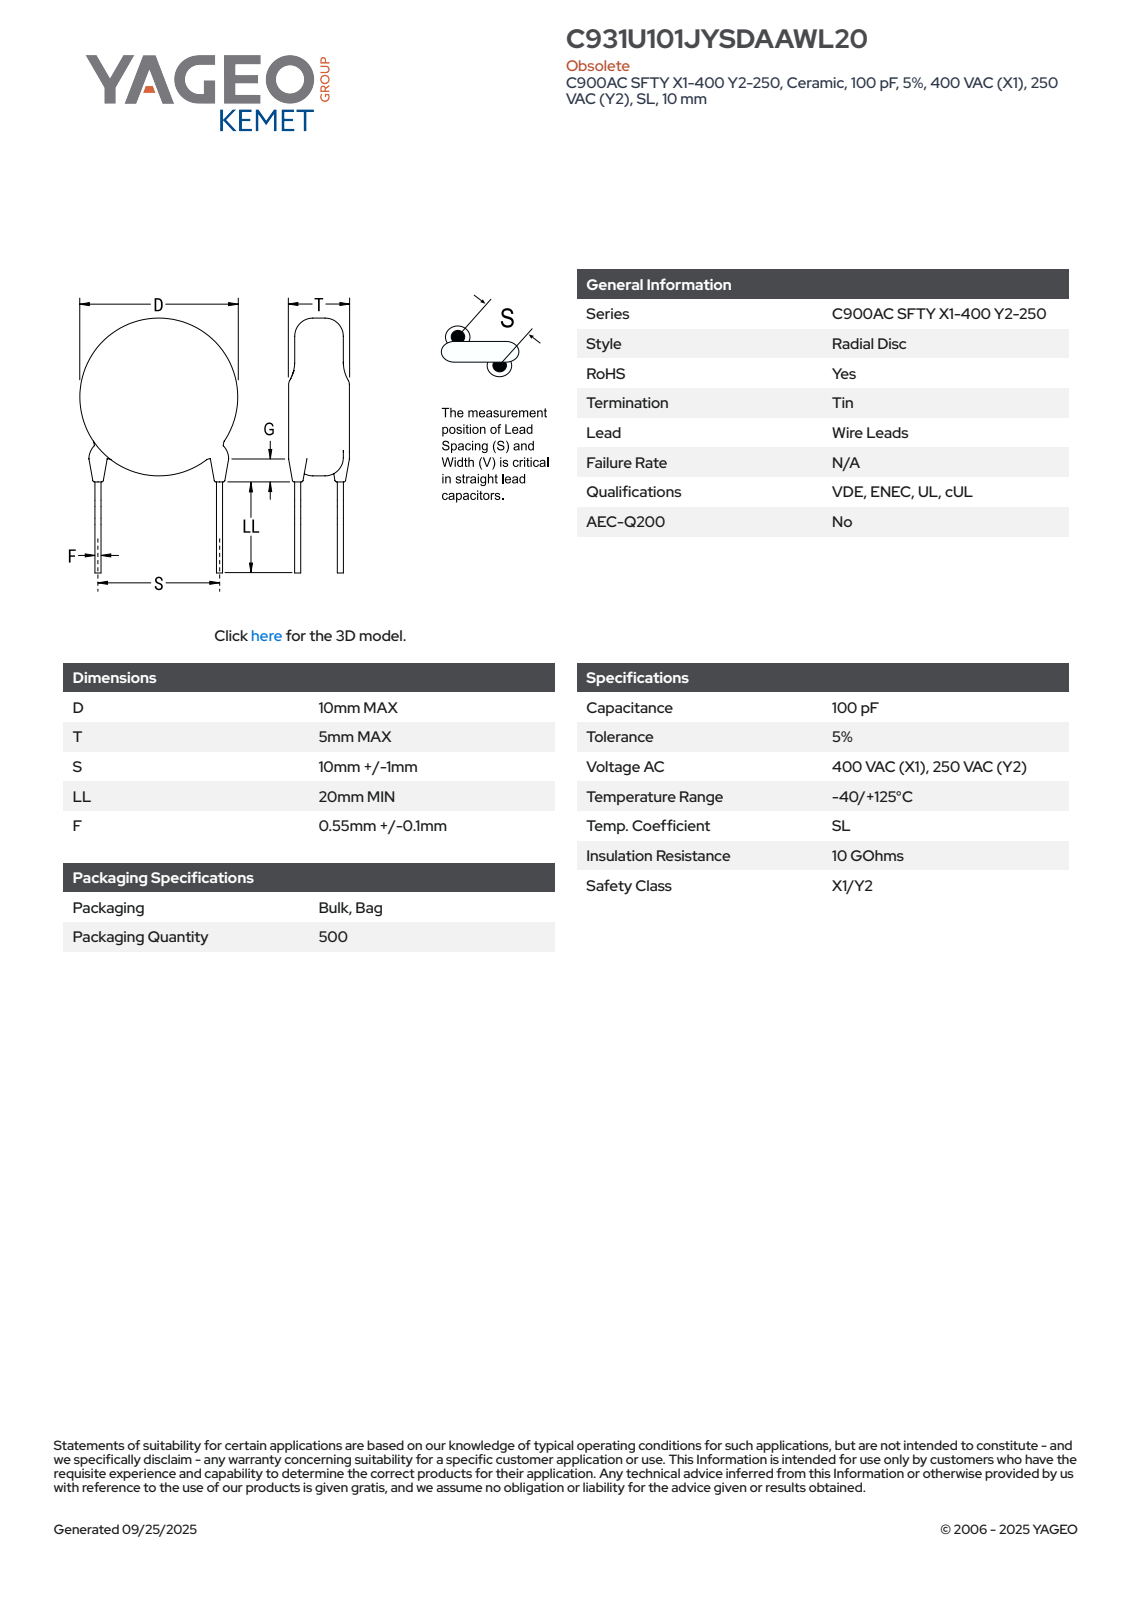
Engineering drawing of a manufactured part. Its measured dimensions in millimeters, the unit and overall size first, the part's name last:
Units: millimetres
Overall size (bounding box): 30.37 × 10.41 × 5
Round bosses / shafts (diameter × count): ⌀0.65 ×2, ⌀10 ×1
Main face-to-face distances: 5, 25.94, 24.79, 1.15, 0.93, 0.42, 0.31, 3.43, 3.56, 1.89
Volume: 397 mm³ · Surface area: 389 mm²
Bodies: 4 solids, 83 faces (61 planar, 6 cylindrical, 16 other)
Part name (STEP PRODUCT): CCD_STC900_D10T5S10LL20F0.65G3
STEP written by: SolidWorks 2014 (AUTOMOTIVE_DESIGN)
